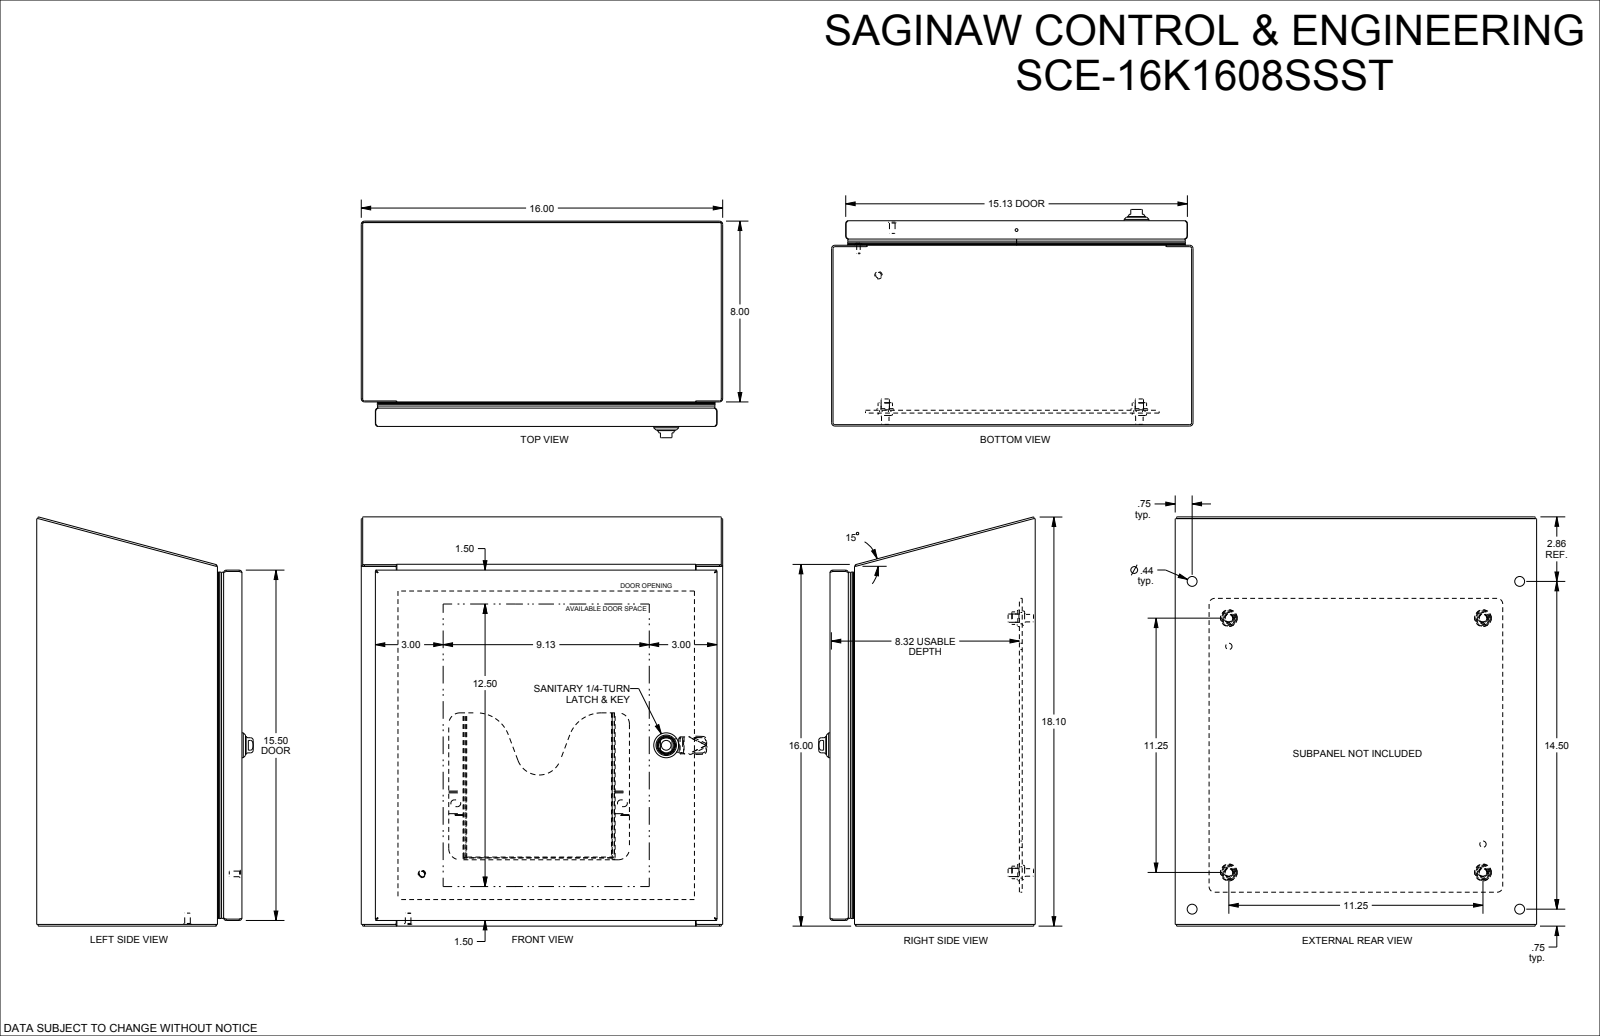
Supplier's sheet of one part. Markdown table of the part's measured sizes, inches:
| quantity | value |
| --- | --- |
| part name | SCE-16K1608SSST |
| STEP written by | SolidWorks 2021 (AUTOMOTIVE_DESIGN) |
| units | inches |
| bodies | 44 solids, 2830 faces (966 planar, 645 cylindrical, 1219 other) |
| overall size | 18.106 × 16 × 9.584 |
| volume | 141.6 in³ |
| surface area | 3 321 in² |
| round holes (diameter × count) | 0.156 × 4, 0.201 × 4, 0.25 × 4, 0.367 × 4, 0.437 × 4, 0.5 × 4, 0.266 × 2, 0.281 × 2, 0.41 × 2, 0.197 × 1, 0.206 × 1, 0.315 × 1 |
| round bosses / shafts (diameter × count) | 0.248 × 6, 0.563 × 4, 0.366 × 4, 0.332 × 4, 0.156 × 4, 0.196 × 3, 1.102 × 1, 0.906 × 1 |
| partial cylindrical surfaces (radius × count) | 0.03 × 64, 0.01 × 28, 0.029 × 24, 0.04 × 21, 0.25 × 20, 0.02 × 16, 0.05 × 16, 0.07 × 14 |
| main face-to-face distances | 0.075, 0.06, 9.024, 8.949, 15.925, 9.084, 9.009, 0.5, 0.625, 0.7 |
| hole center spacings | 1.769, 12.977, 14.5, 9.5, 0.985, 1.247, 1.25, 2.055 |
